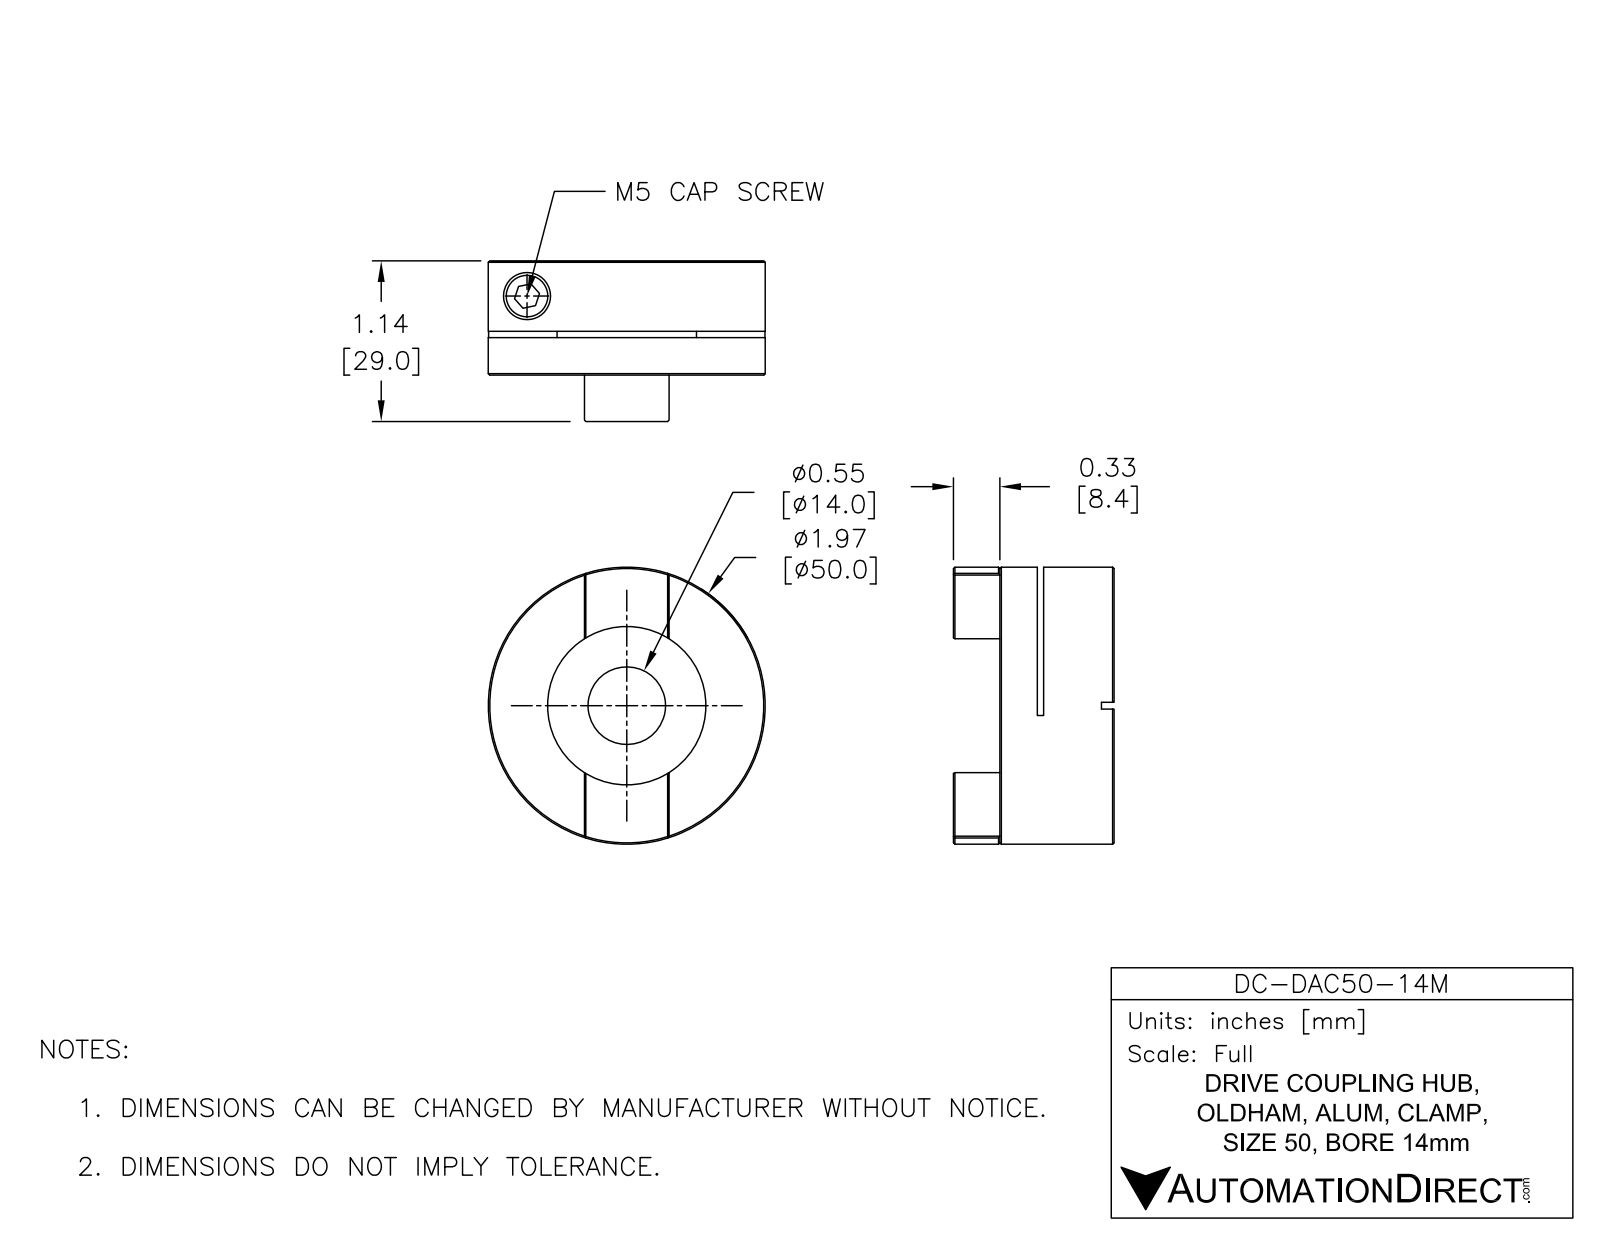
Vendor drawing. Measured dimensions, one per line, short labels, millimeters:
name: DC-DAC50-14M
written by: SolidWorks 2015 (AUTOMOTIVE_DESIGN)
unit: mm
bodies: 1 solid, 58 faces (31 planar, 19 cylindrical, 8 other)
size: 50 × 50 × 28.98
volume: 36 051 mm³; area: 11 907 mm²
holes: 1× ⌀5.51, 1× ⌀10.01, 1× ⌀14, 1× ⌀28.57
bosses: 1× ⌀50, 1× ⌀49.49
rounds: 1× R25.4
face distances: 13.84, 20.6, 6.76, 12.7, 1.14, 7.9, 18.82, 6.12, 4.98, 1.78
